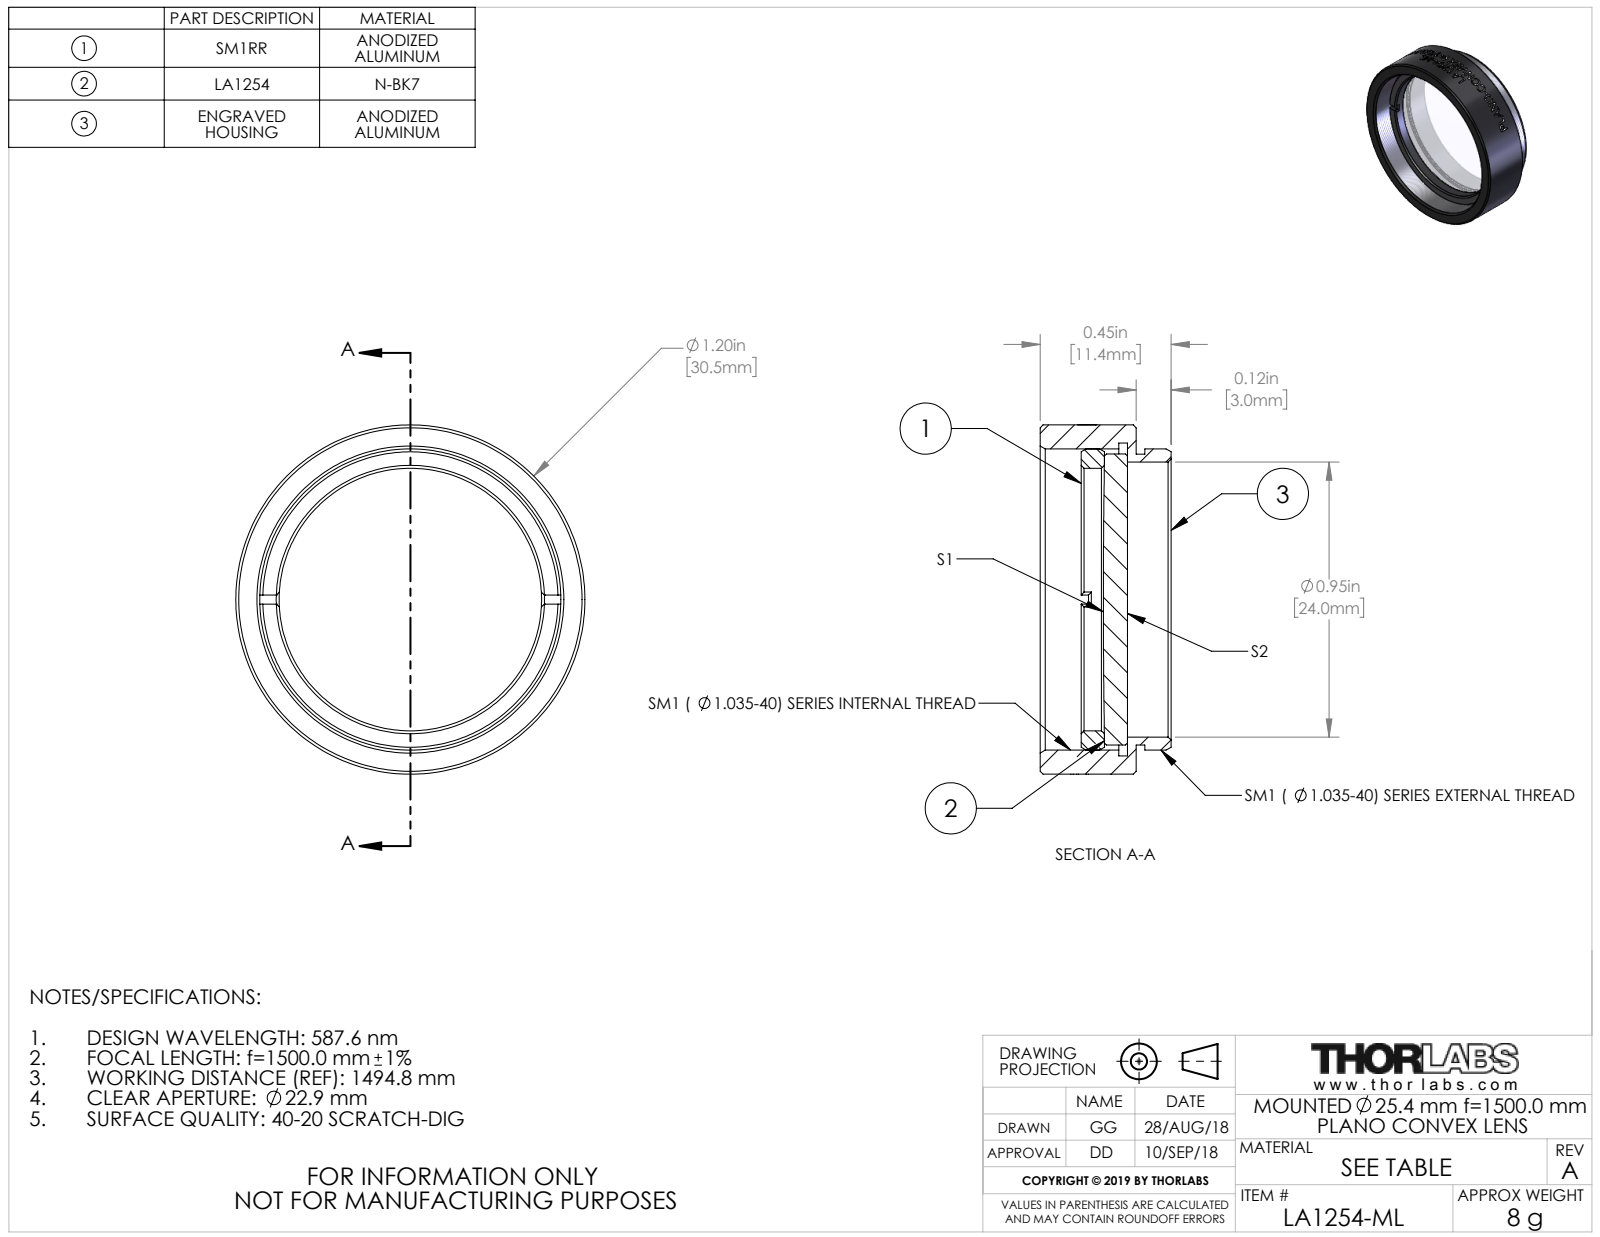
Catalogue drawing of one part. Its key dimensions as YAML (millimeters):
part_name: "TTN162134-E0W"
step_written_by: "SolidWorks 2018 (CONFIG_CONTROL_DESIGN)"
units: millimeters
bodies: {solids: 3, faces: 138, planar: 20, cylindrical: 90, other: 28}
overall_size: [30.48, 30.48, 11.43]
volume: 3116
surface_area: 4296
round_holes:
  - {diameter: 22.91, count: 1}
  - {diameter: 24, count: 1}
  - {diameter: 27.3, count: 1}
round_bosses_or_shafts:
  - {diameter: 30.48, count: 1}
  - {diameter: 26.29, count: 1}
  - {diameter: 25.4, count: 1}
  - {diameter: 25.37, count: 1}
face_to_face_distances: [0.77, 8.39, 7.62, 2.78, 2.01, 5.61, 4.81, 4.04, 2.03, 3.58]
